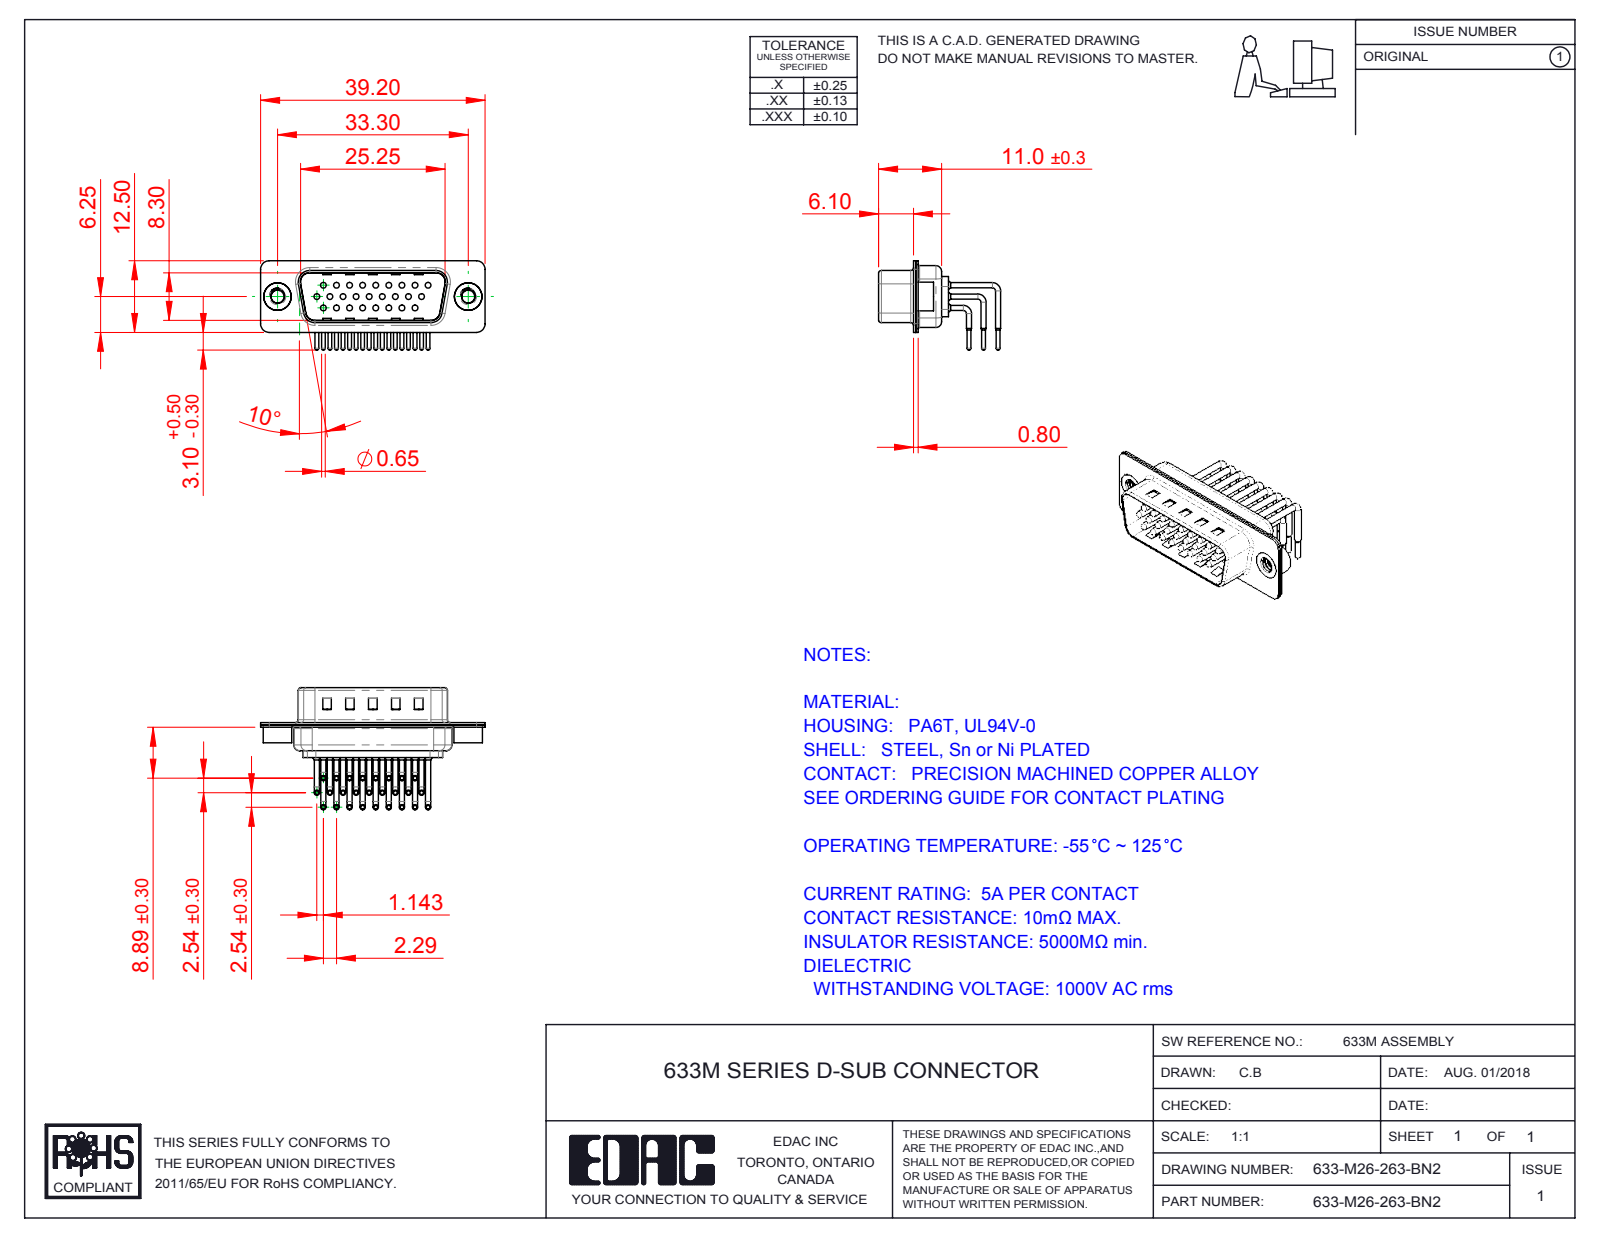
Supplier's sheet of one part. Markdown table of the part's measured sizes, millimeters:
| quantity | value |
| --- | --- |
| part name | 633M Contact Row 2; 633M Contact Row 3; 633M 4-40 Threaded Rivet; 633M Housing_26 Contacts (+4 more) |
| STEP written by | SolidWorks 2016 (CONFIG_CONTROL_DESIGN) |
| units | millimeters |
| bodies | 31 solids, 3200 faces (1803 planar, 1069 cylindrical, 328 other) |
| overall size | 39.2 × 21.32 × 15.6 |
| volume | 2 091 mm³ |
| surface area | 6 696 mm² |
| round holes (diameter × count) | 1 × 26, 1.7 × 26, 2 × 26, 2.26 × 2, 4 × 2, 4.8 × 2 |
| round bosses / shafts (diameter × count) | 0.9 × 52, 1.5 × 26, 0.65 × 26, 5 × 2, 4.9 × 2 |
| partial cylindrical surfaces (radius × count) | 1.01 × 26, 1.5 × 16, 2 × 12, 0.5 × 8, 1.6 × 8, 0.25 × 4, 0.6 × 4, 0.65 × 4 |
| main face-to-face distances | 0.4, 0.85, 9.55, 1.5, 8.7, 1.9, 1.25, 10.4, 0.8, 0.35 |
| hole center spacings | 3.96, 2.28, 4.57, 6.05, 2.29, 8.24, 6.86, 10.48 |
